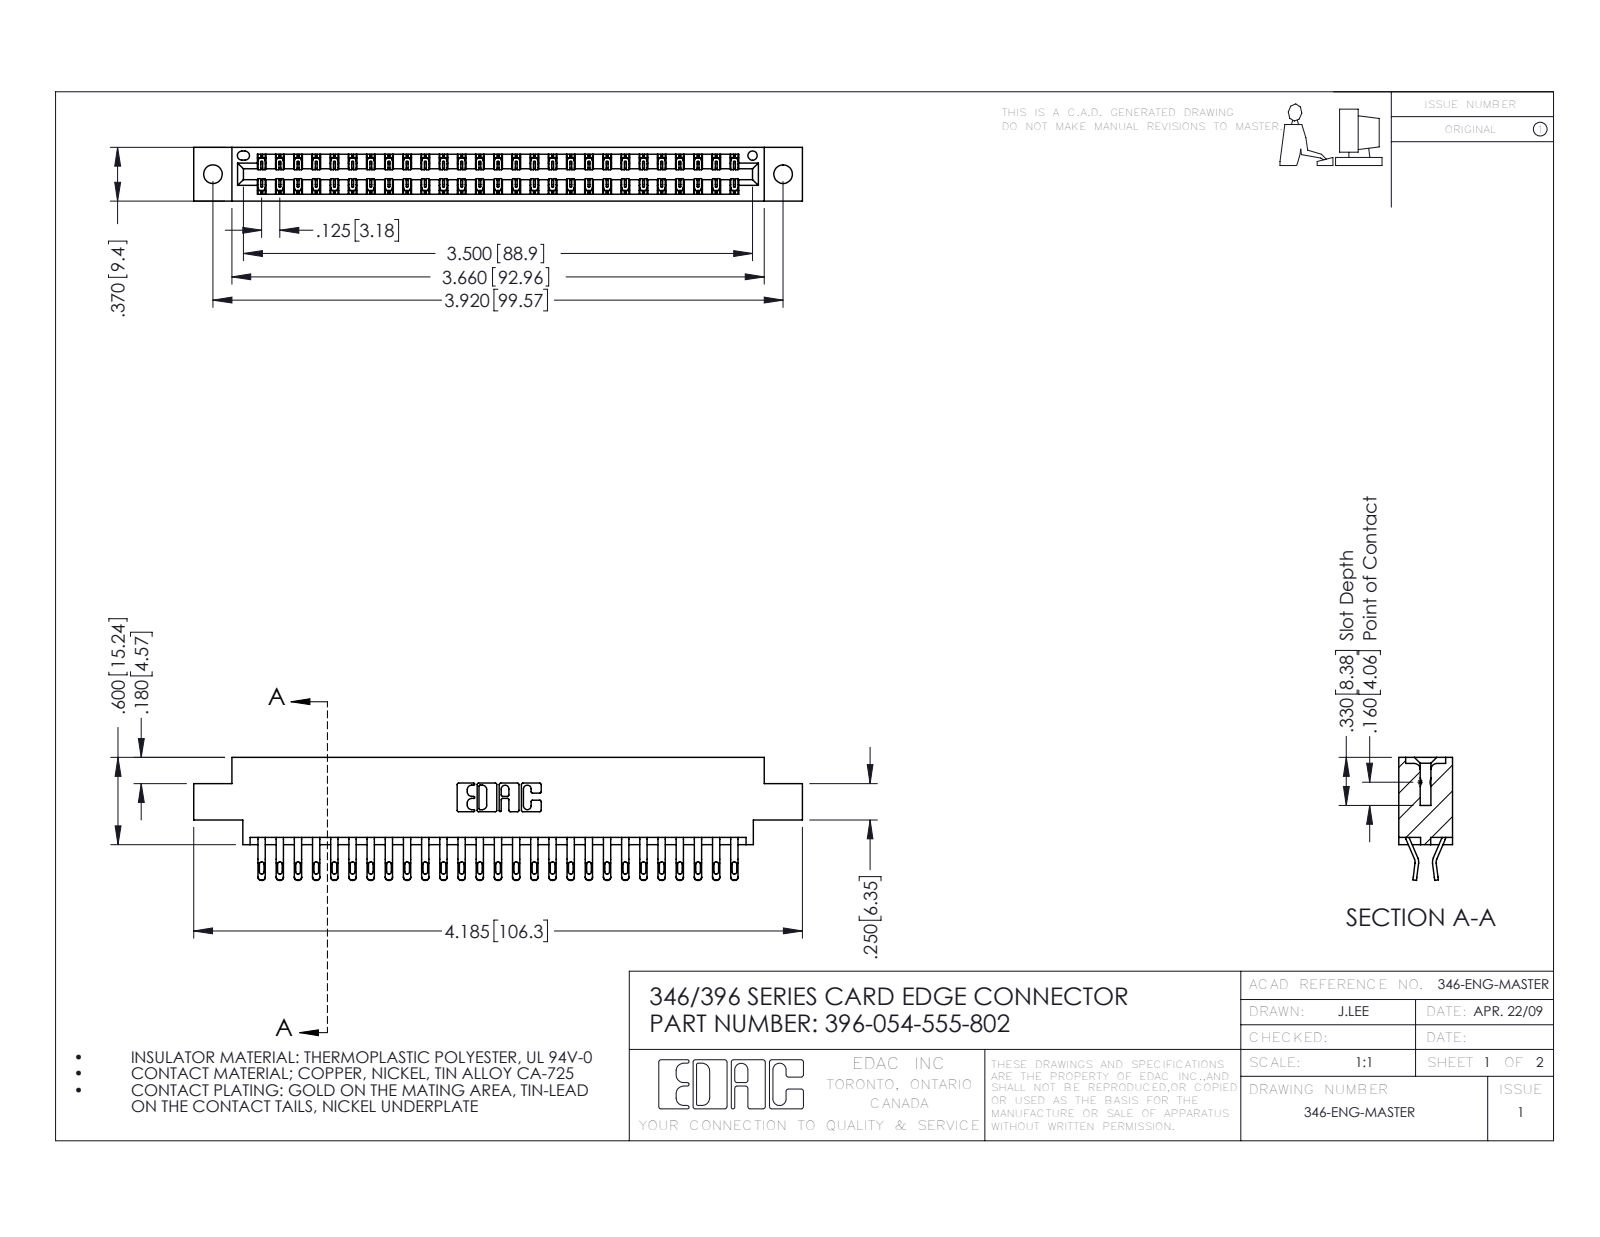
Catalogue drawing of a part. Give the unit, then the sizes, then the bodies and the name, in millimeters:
Units: millimetres
Overall size (bounding box): 106.3 × 21.5 × 9.4
Round holes (diameter × count): ⌀3.3 ×2, ⌀1.6 ×1
Partial cylindrical surfaces — rounded edges, fillets, slot ends (radius × count): R0.4 ×108, R0.5 ×108, R0.2 ×81, R0.3 ×22, R0.2 ×6, R0.8 ×6, R0.7 ×3, R0.3 ×2
Main face-to-face distances: 1.2, 8.2, 9.4, 6.4, 0.6, 1.8, 7.6, 7, 3.8, 5.6
Hole centre spacings: 6.2, 94.3, 99.6
Volume: 10 200 mm³ · Surface area: 14 270 mm²
Bodies: 55 solids, 3258 faces (1862 planar, 1396 cylindrical, 0 other)
Part name (STEP PRODUCT): 345-292-001_555 Tail; 396-054-555-802; 346 Part_0.170 Offset - 0.128 Dia
STEP written by: SolidWorks 2016 (CONFIG_CONTROL_DESIGN)
